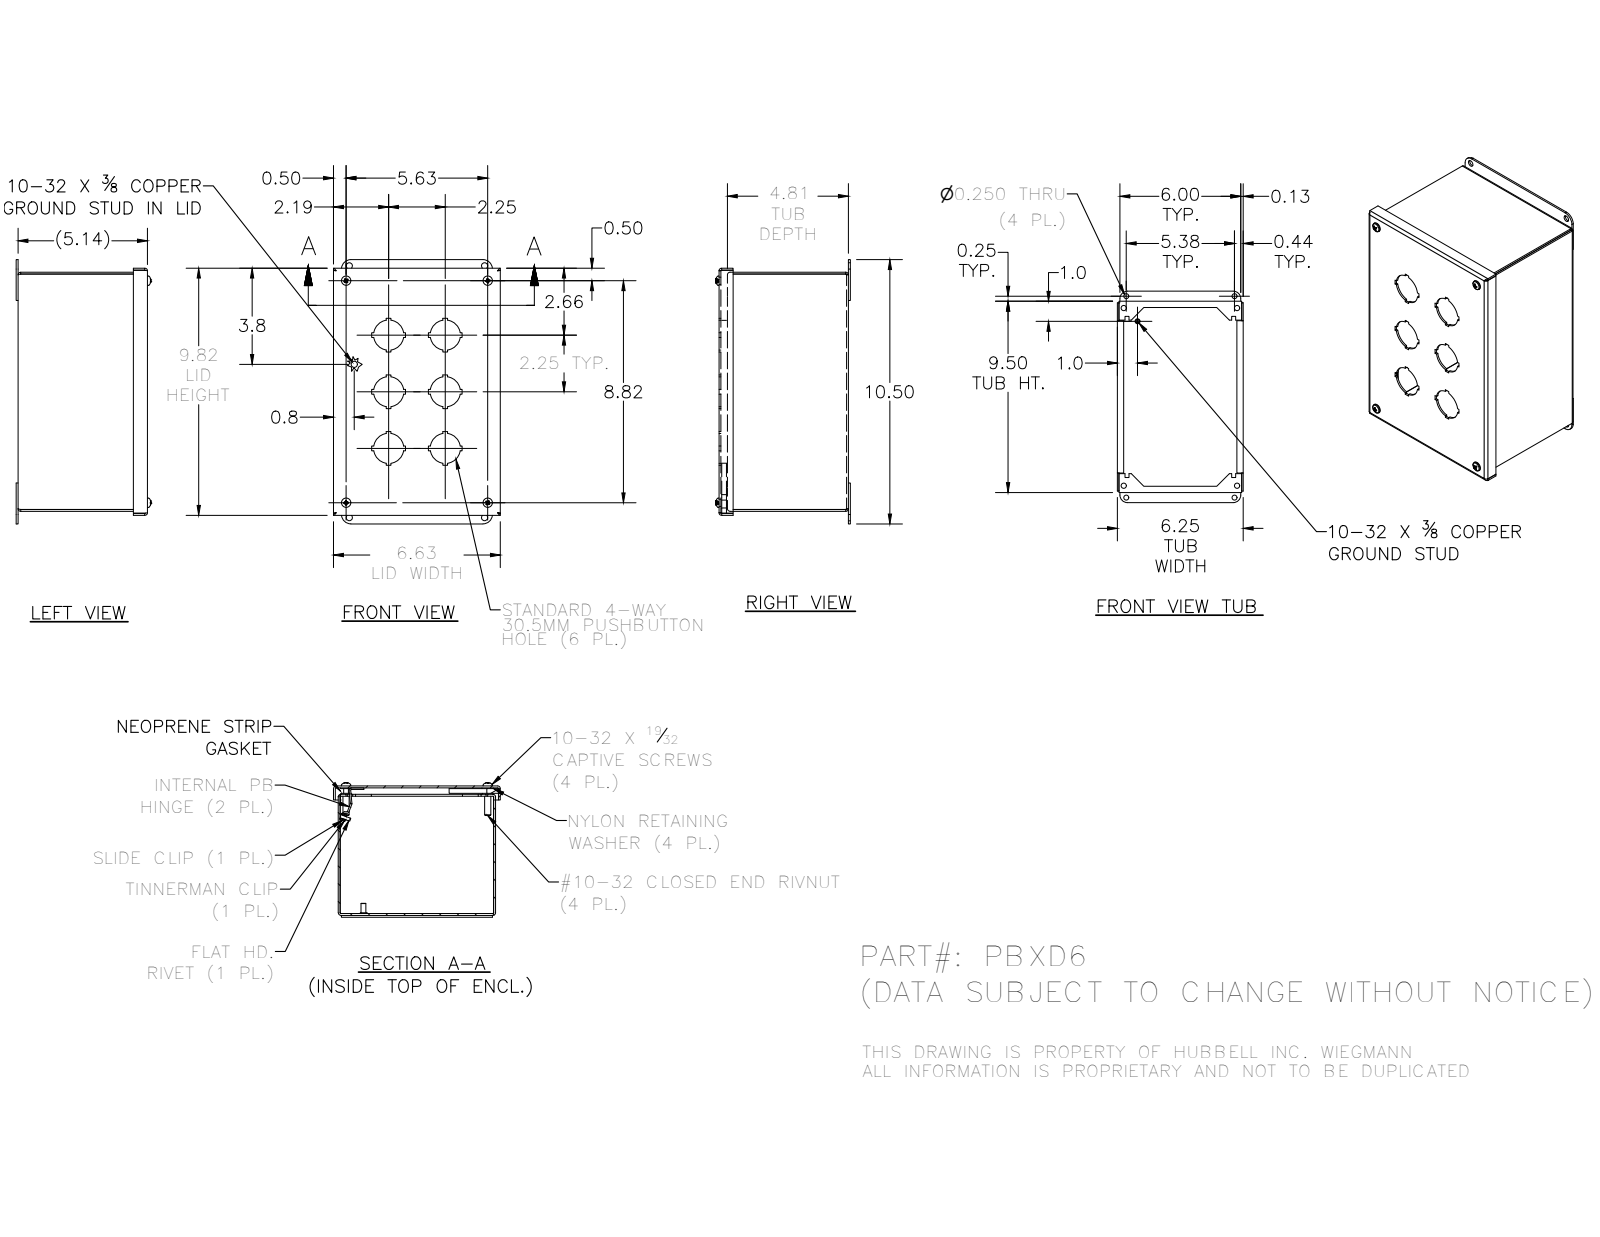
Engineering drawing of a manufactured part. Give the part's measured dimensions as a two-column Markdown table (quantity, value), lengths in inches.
| quantity | value |
| --- | --- |
| part name | PBXD6LID; 372163; 39077; PBXD6BKP (+8 more) |
| STEP written by | Autodesk Inventor 2016 (AUTOMOTIVE_DESIGN) |
| units | inches |
| bodies | 25 solids, 695 faces (427 planar, 154 cylindrical, 114 other) |
| overall size | 10.5 × 6.63 × 5.346 |
| volume | 23.8 in³ |
| surface area | 653 in² |
| round holes (diameter × count) | 1.2 × 6, 0.156 × 4, 0.196 × 4, 0.25 × 4, 0.257 × 4, 0.278 × 4, 0.281 × 4, 0.14 × 2, 0.313 × 2 |
| round bosses / shafts (diameter × count) | 0.19 × 6, 0.453 × 4, 0.406 × 4, 0.373 × 4, 0.248 × 4, 0.25 × 3, 0.125 × 1 |
| partial cylindrical surfaces (radius × count) | 0.031 × 12, 0.105 × 12, 0.188 × 6, 0.089 × 4, 0.09 × 4, 0.375 × 4, 0.031 × 3, 0.063 × 3 |
| main face-to-face distances | 0.074, 5.068, 6.176, 5.142, 9.426, 4.994, 6.102, 6.25, 9.5, 9.352 |
| hole center spacings | 2.25, 3.163, 3.182, 5.239, 6.871, 7.417, 9.411, 0.051 |
